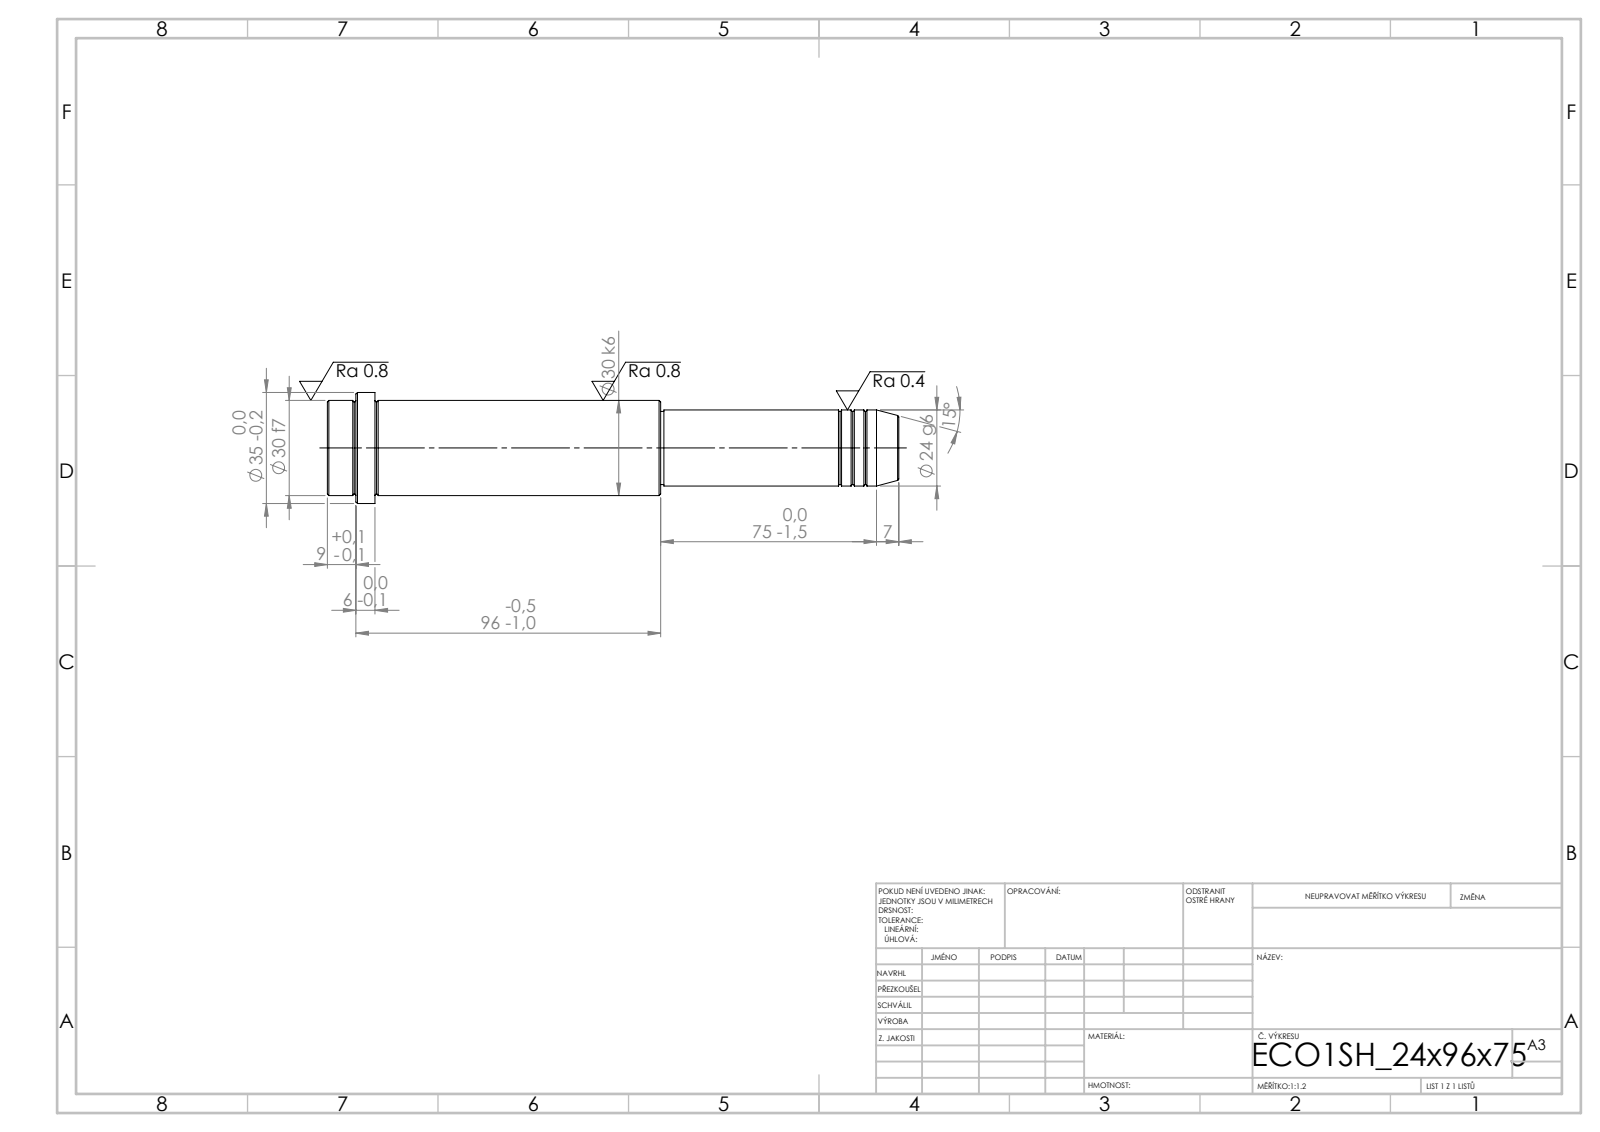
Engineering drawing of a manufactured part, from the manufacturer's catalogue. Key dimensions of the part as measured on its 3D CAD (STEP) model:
STEP written by: SolidWorks 2019 (CONFIG_CONTROL_DESIGN)
Units: millimetres
Bodies: 1 solid, 52 faces (6 planar, 16 cylindrical, 30 other)
Overall size (bounding box): 180 × 35 × 35
Volume: 108 976 mm³ · Surface area: 17 611 mm²
Round bosses / shafts (diameter × count): ⌀35 ×1, ⌀30 ×1, ⌀24 ×1, ⌀23 ×1
Main face-to-face distances: 180, 165, 15, 75, 90, 105, 171, 96, 6, 9
